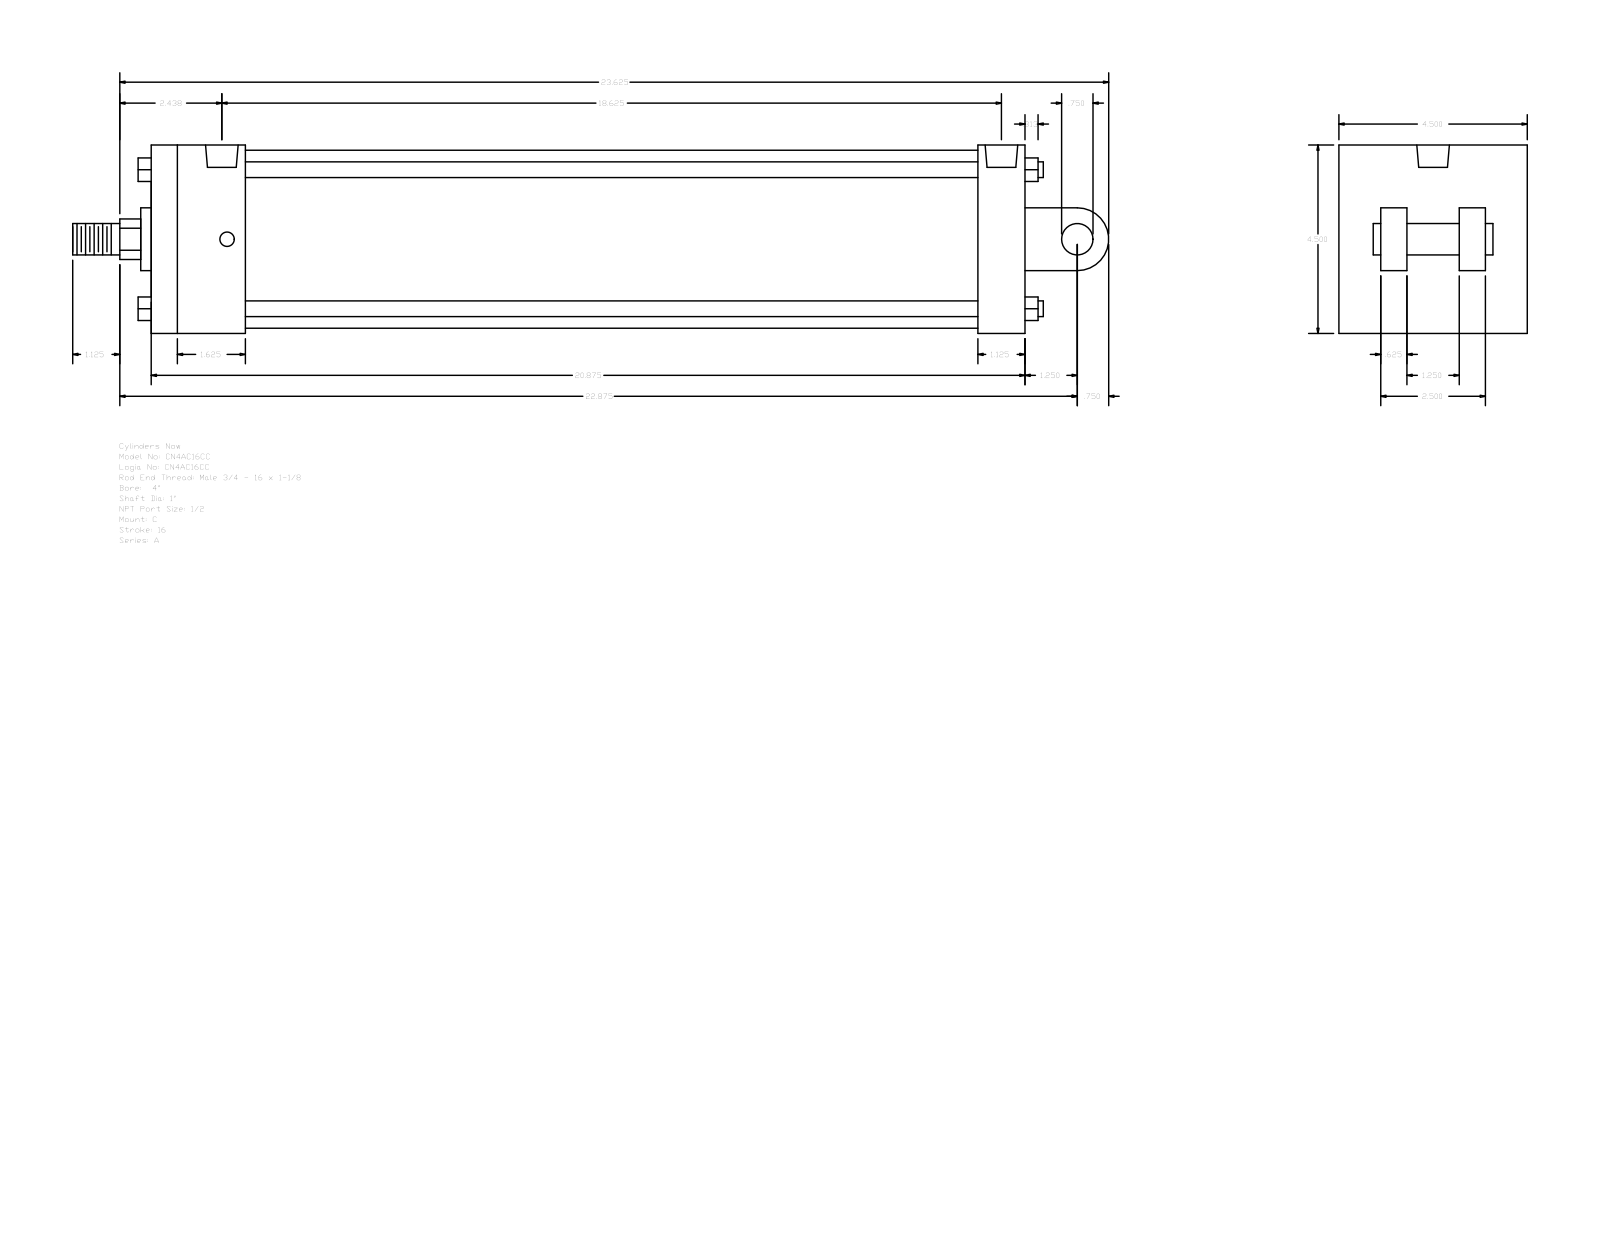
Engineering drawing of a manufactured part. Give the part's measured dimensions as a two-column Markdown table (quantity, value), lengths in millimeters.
| quantity | value |
| --- | --- |
| part name | A_C__0400_1 |
| STEP written by | GSSL Pune (CONFIG_CONTROL_DESIGN) |
| units | millimeters |
| bodies | 0 solids, 135 faces (102 planar, 33 cylindrical, 0 other) |
| overall size | 628.65 × 114.3 × 114.3 |
| round holes (diameter × count) | 8.73 × 4, 19.77 × 2 |
| round bosses / shafts (diameter × count) | 9.53 × 4, 19.05 × 2, 107.95 × 1, 38.1 × 1, 25.4 × 1 |
| partial cylindrical surfaces (radius × count) | 12.29 × 1, 19.05 × 1 |
| main face-to-face distances | 114.3, 530.22, 73.03, 28.57, 501.65, 57.15, 444.5, 473.07, 41.27, 38.1 |
| hole center spacings | 3.18, 466.72, 469.9, 473.08 |
